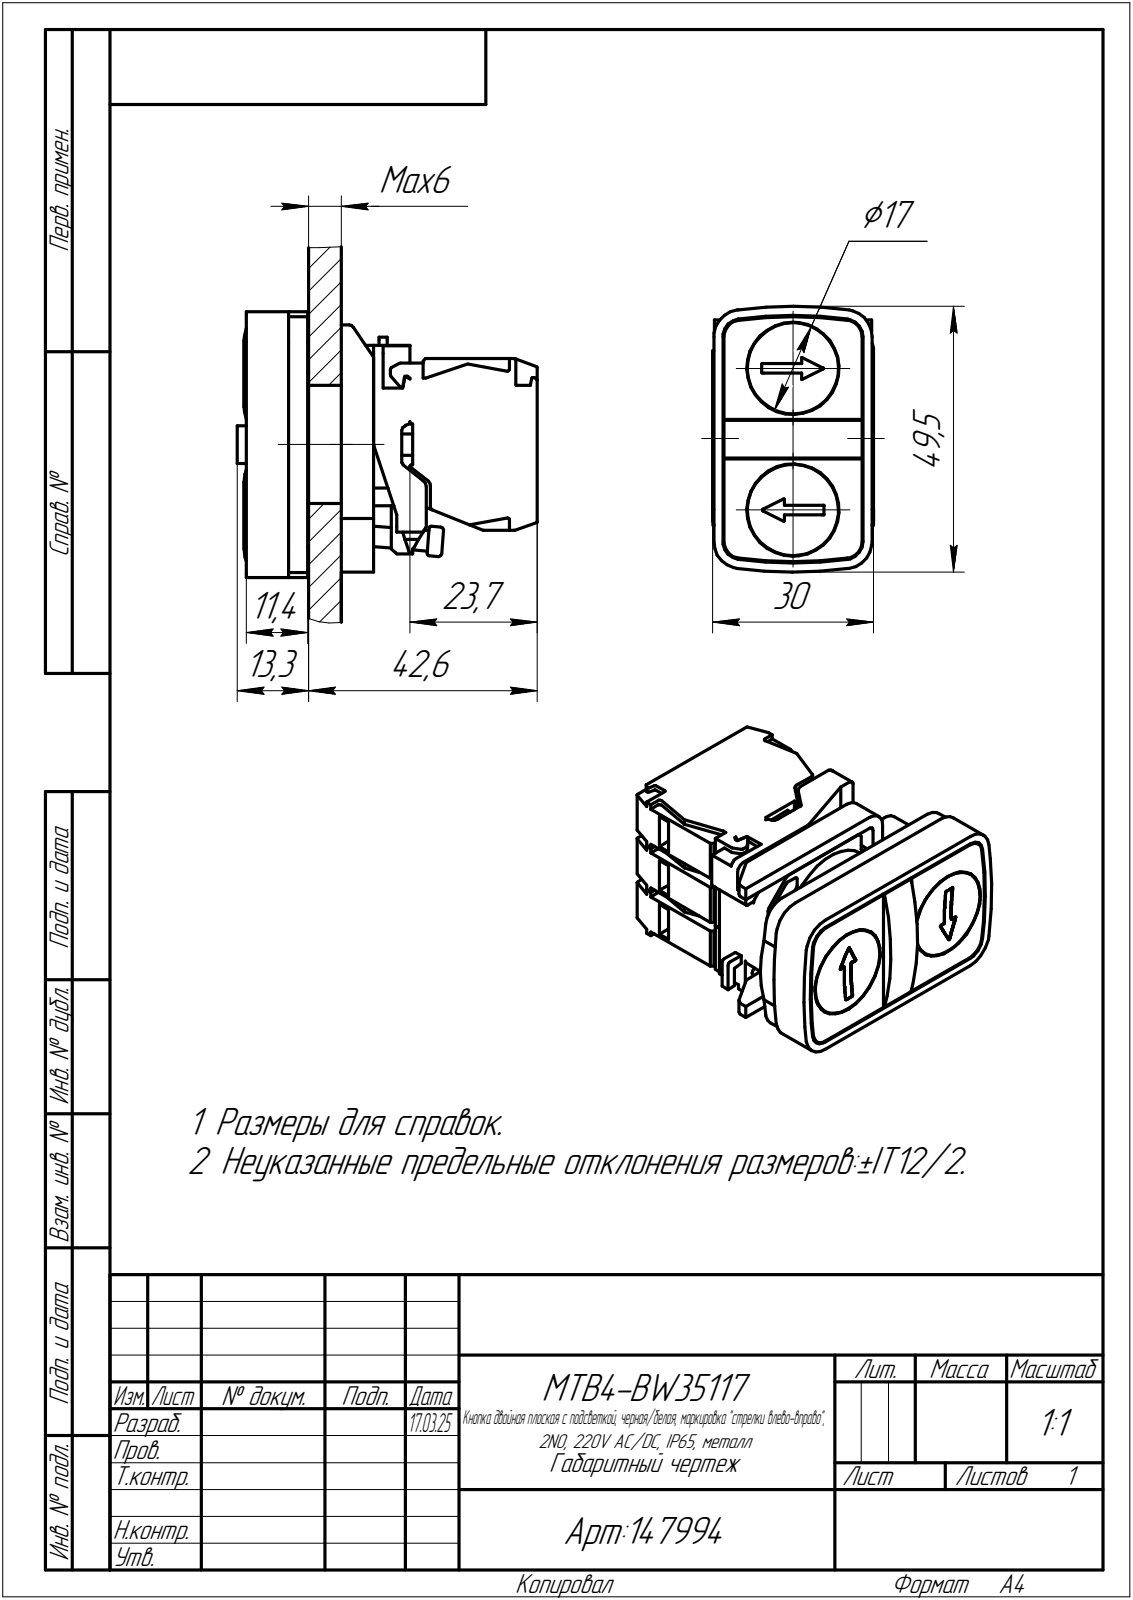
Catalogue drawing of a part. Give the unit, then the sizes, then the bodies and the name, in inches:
Units: inches
Overall size (bounding box): 2.201 × 1.949 × 1.181
Round holes (diameter × count): ⌀0.059 ×2, ⌀0.236 ×2, ⌀0.677 ×2, ⌀0.807 ×1
Round bosses / shafts (diameter × count): ⌀0.669 ×2, ⌀1.055 ×1, ⌀0.866 ×1, ⌀0.217 ×1, ⌀0.15 ×1
Partial cylindrical surfaces — rounded edges, fillets, slot ends (radius × count): R0.02 ×23, R0.004 ×10, R0.008 ×10, R0.031 ×7, R0.039 ×5, R0.04 ×4, R0.122 ×4, R0.13 ×4
Main face-to-face distances: 0.394, 0.39, 0.787, 0.783, 0.398, 0.449, 0.098, 1.177, 0.072, 0.384
Hole centre spacings: 0.185, 0.335, 0.52, 0.854, 0.455, 0.468, 0.497, 0.542
Volume: 2.954 in³ · Surface area: 32.24 in²
Bodies: 2 solids, 668 faces (426 planar, 204 cylindrical, 38 other)
Part name (STEP PRODUCT): LA167-B4-BWA3512315-24V
STEP written by: PRO/ENGINEER BY PARAMETRIC TECHNOLOGY CORPORATION, 2010280 (CONFIG_CONTROL_DESIGN)
